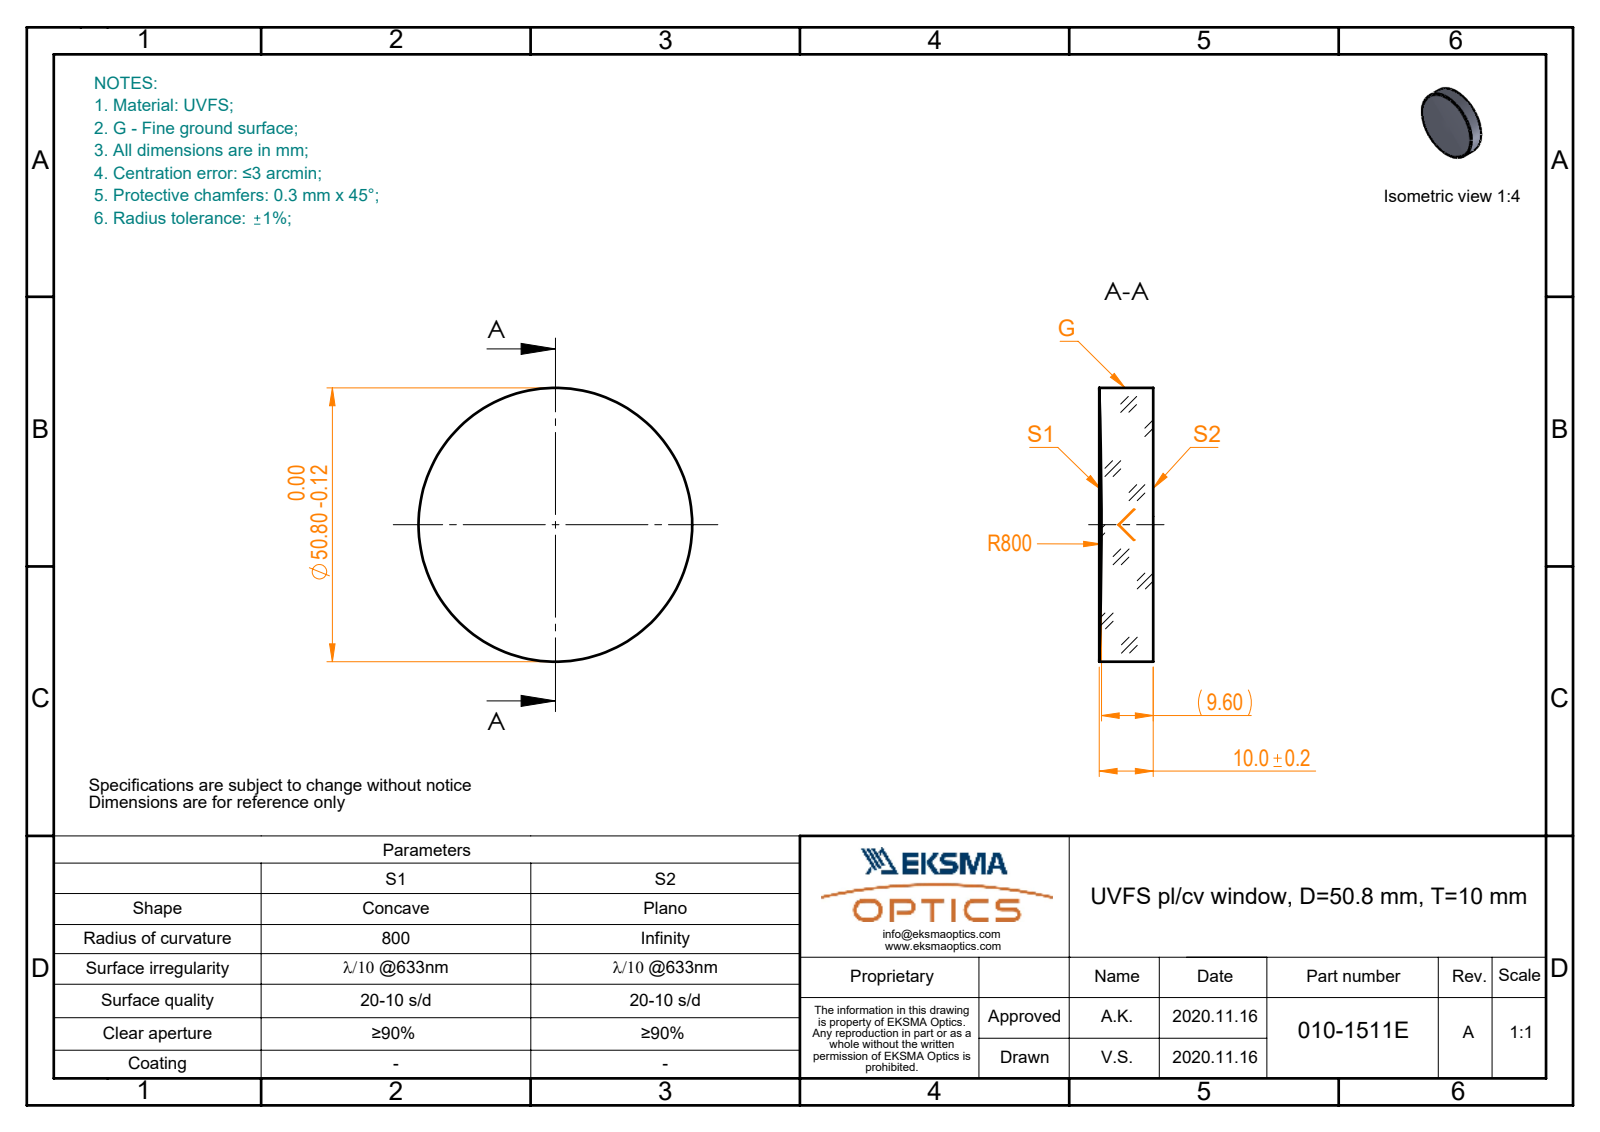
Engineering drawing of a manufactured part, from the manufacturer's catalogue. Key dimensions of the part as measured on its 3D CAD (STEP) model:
Part name (STEP PRODUCT): 010-1511E_UVFS_PCV_window
STEP written by: SolidWorks 2019 (CONFIG_CONTROL_DESIGN)
Units: millimetres
Bodies: 1 solid, 5 faces (1 planar, 2 cylindrical, 2 other)
Overall size (bounding box): 50.8 × 50.8 × 10
Volume: 19 860 mm³ · Surface area: 5 650 mm²
Round bosses / shafts (diameter × count): ⌀50.8 ×1
